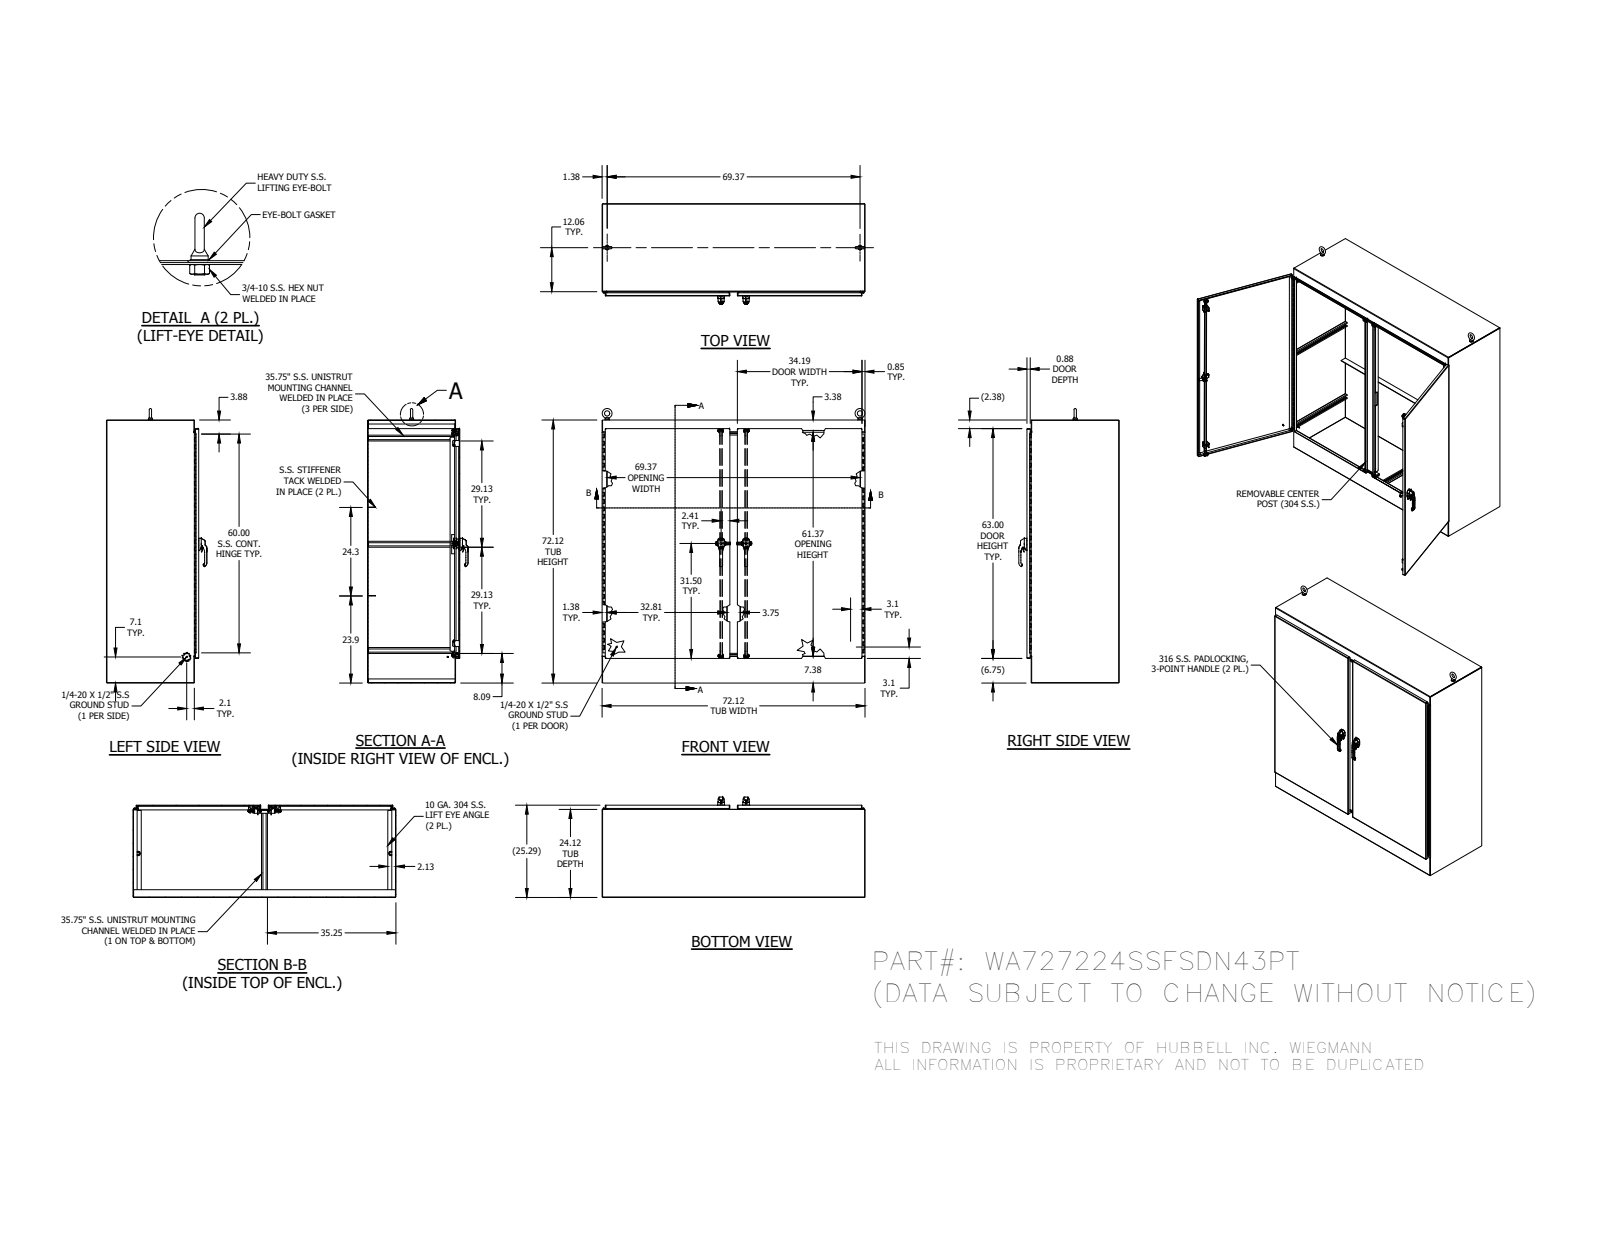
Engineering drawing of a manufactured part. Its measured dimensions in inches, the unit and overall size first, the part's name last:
Units: inches
Overall size (bounding box): 75.248 × 72.125 × 27.541
Round holes (diameter × count): ⌀0.262 ×16, ⌀0.375 ×16, ⌀0.187 ×8, ⌀0.213 ×6, ⌀0.25 ×6, ⌀0.281 ×6, ⌀0.196 ×4, ⌀0.241 ×4, ⌀0.252 ×4, ⌀0.281 ×4, ⌀0.315 ×4, ⌀0.4 ×4
Round bosses / shafts (diameter × count): ⌀0.25 ×7, ⌀1 ×6, ⌀0.533 ×6, ⌀0.236 ×6, ⌀0.563 ×4, ⌀0.531 ×4, ⌀0.5 ×4, ⌀0.438 ×4
Partial cylindrical surfaces — rounded edges, fillets, slot ends (radius × count): R0.02 ×352, R0.012 ×214, R0.019 ×44, R0.125 ×44, R0.05 ×34, R0.079 ×28, R0.025 ×24, R0.059 ×24
Main face-to-face distances: 0.125, 0.125, 72, 25.167, 71.875, 72.125, 24, 1.167, 25.042, 25.165
Hole centre spacings: 54.49, 55.24, 20, 0.38, 0.38, 6.667, 0.76, 13.333
Volume: 2 578 in³ · Surface area: 41 954 in²
Bodies: 133 solids, 7024 faces (2638 planar, 2690 cylindrical, 1696 other)
Part name (STEP PRODUCT): 30254; WA7272SSFSDN43PTLDRASSM; PLASTIC-ROLLER-CAM_AF0_ASM; WA72SSFSDN43PTSTFNR (+8 more)
STEP written by: SolidWorks 2014 (AUTOMOTIVE_DESIGN)
